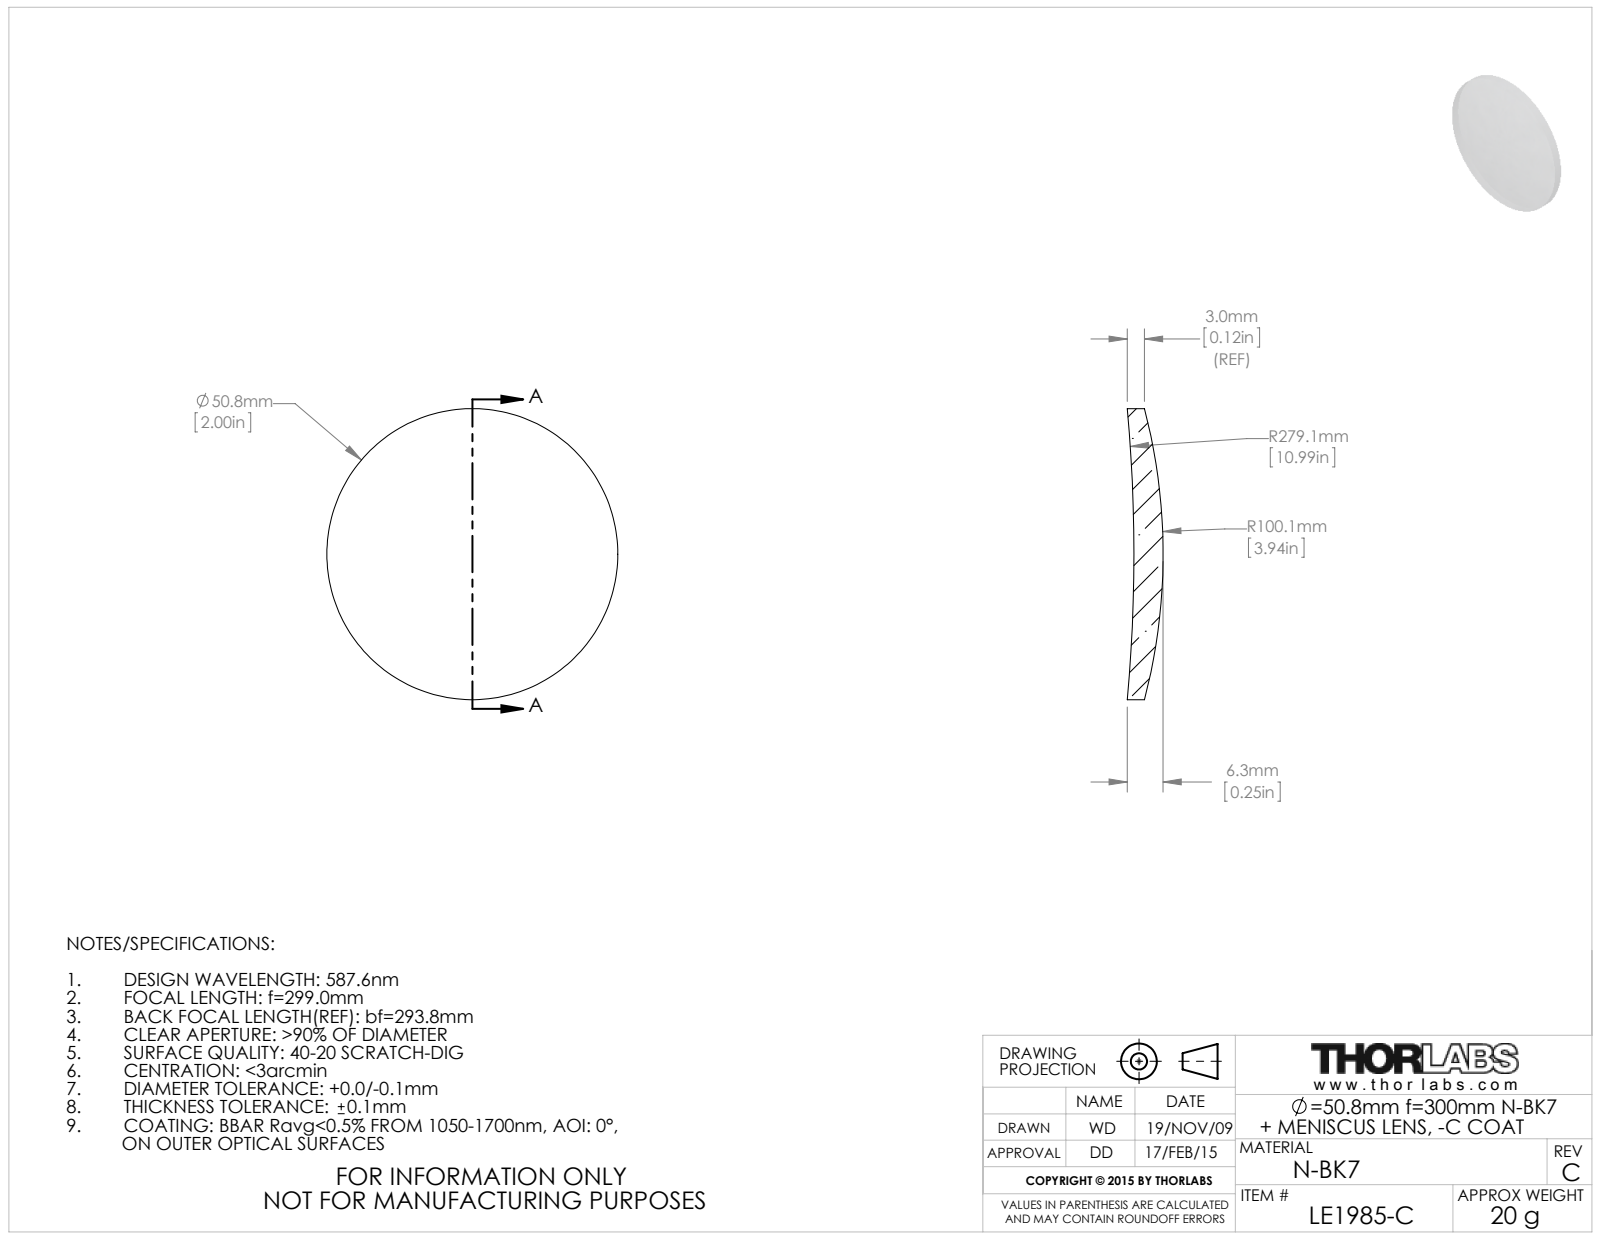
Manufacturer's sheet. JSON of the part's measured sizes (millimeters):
{"part_name": "4864-E0W", "step_written_by": "SolidWorks 2009 (AUTOMOTIVE_DESIGN)", "units": "millimeters", "bodies": {"solids": 1, "faces": 6, "planar": 0, "cylindrical": 2, "other": 4}, "overall_size": [50.8, 50.8, 6.26], "volume_mm3": 8207, "surface_area_mm2": 4567, "round_bosses_or_shafts": [[50.8, 1]]}
